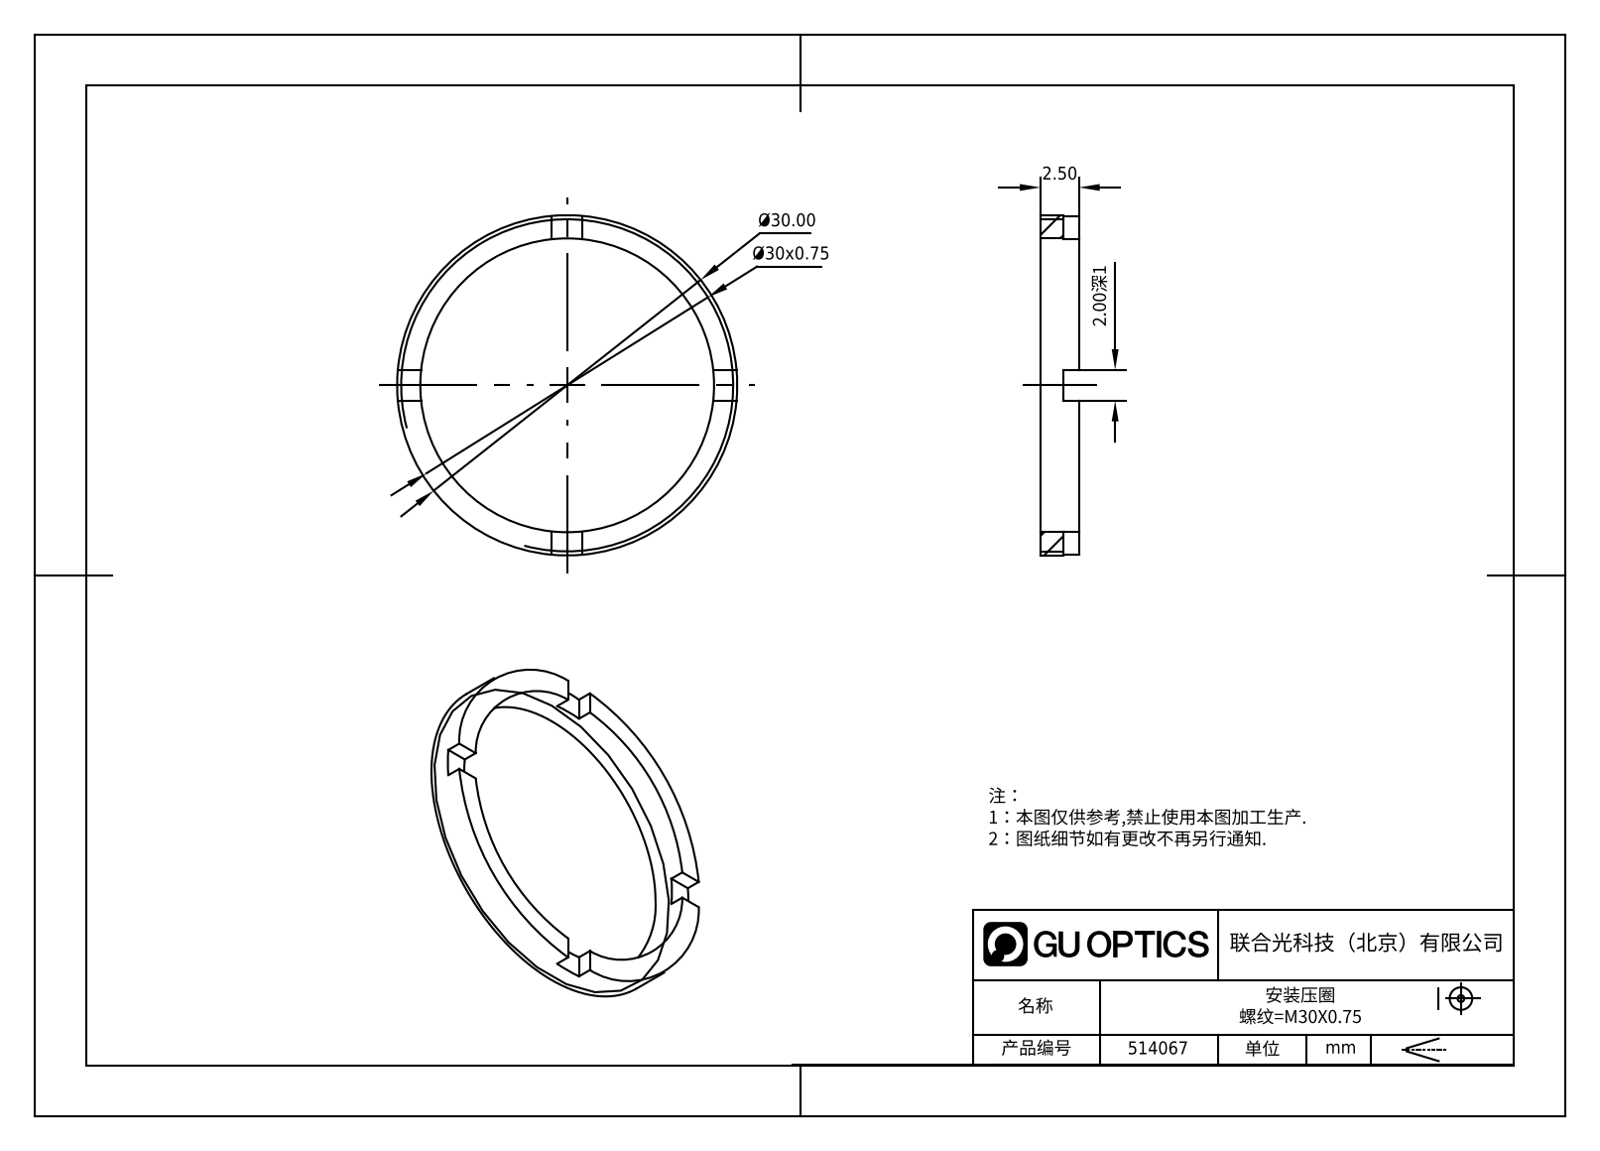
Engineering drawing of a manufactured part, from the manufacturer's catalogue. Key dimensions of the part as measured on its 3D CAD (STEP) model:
Part name (STEP PRODUCT): 514067
STEP written by: SolidWorks 2020 (CONFIG_CONTROL_DESIGN)
Units: millimetres
Bodies: 1 solid, 21 faces (17 planar, 4 cylindrical, 0 other)
Overall size (bounding box): 30 × 30 × 2.5
Volume: 424 mm³ · Surface area: 792 mm²
Round holes (diameter × count): ⌀26 ×1
Round bosses / shafts (diameter × count): ⌀30 ×1
Main face-to-face distances: 2.5, 1.5, 1, 2
